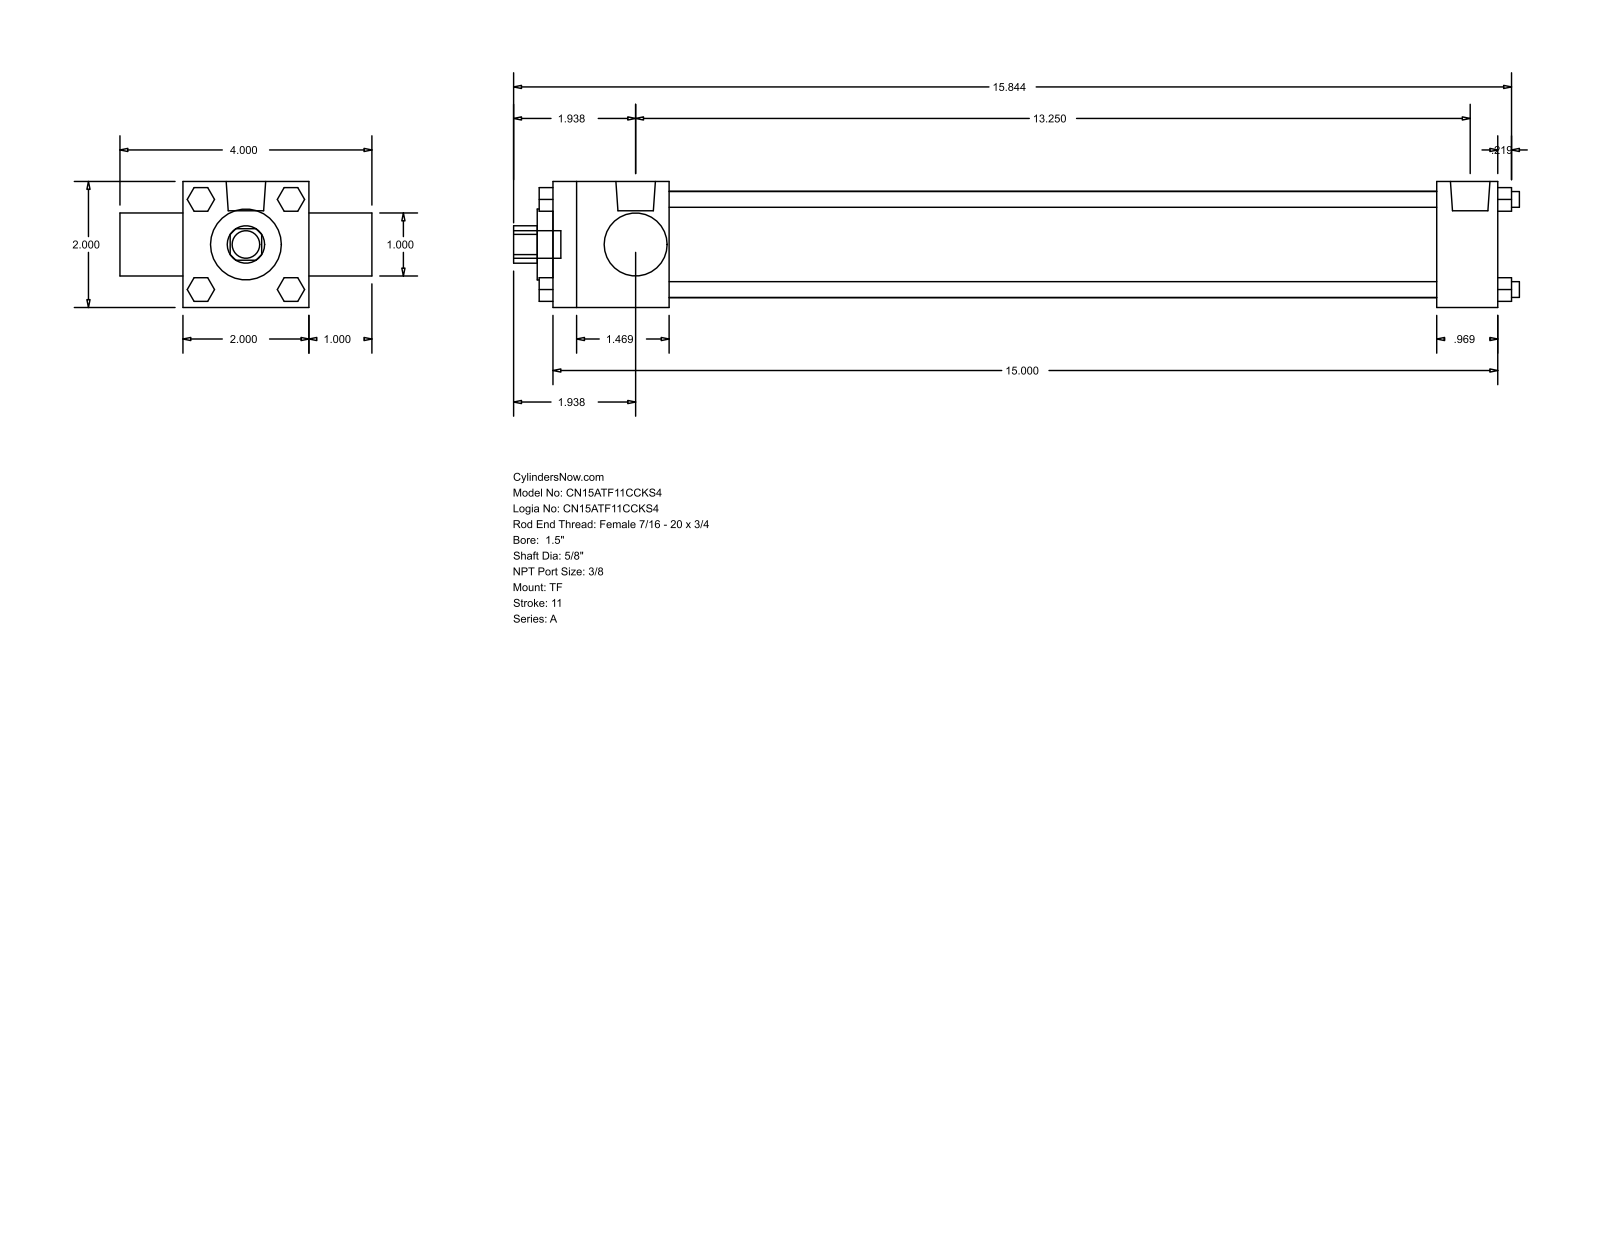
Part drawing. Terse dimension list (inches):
name: A_TF__0150_0.625
written by: GSSL Pune (CONFIG_CONTROL_DESIGN)
unit: in
bodies: 0 solids, 120 faces (92 planar, 28 cylindrical, 0 other)
size: 15.969 × 4 × 2
holes: 1× ⌀0.625, 1× ⌀1, 1× ⌀1.125, 1× ⌀1.69
bosses: 4× ⌀0.25, 3× ⌀0.219, 2× ⌀0.627, 1× ⌀0.437
rounds: 1× R0.297
face distances: 2, 15, 1, 3, 1.844, 14.031, 12.187, 13.156, 0.969, 0.375
